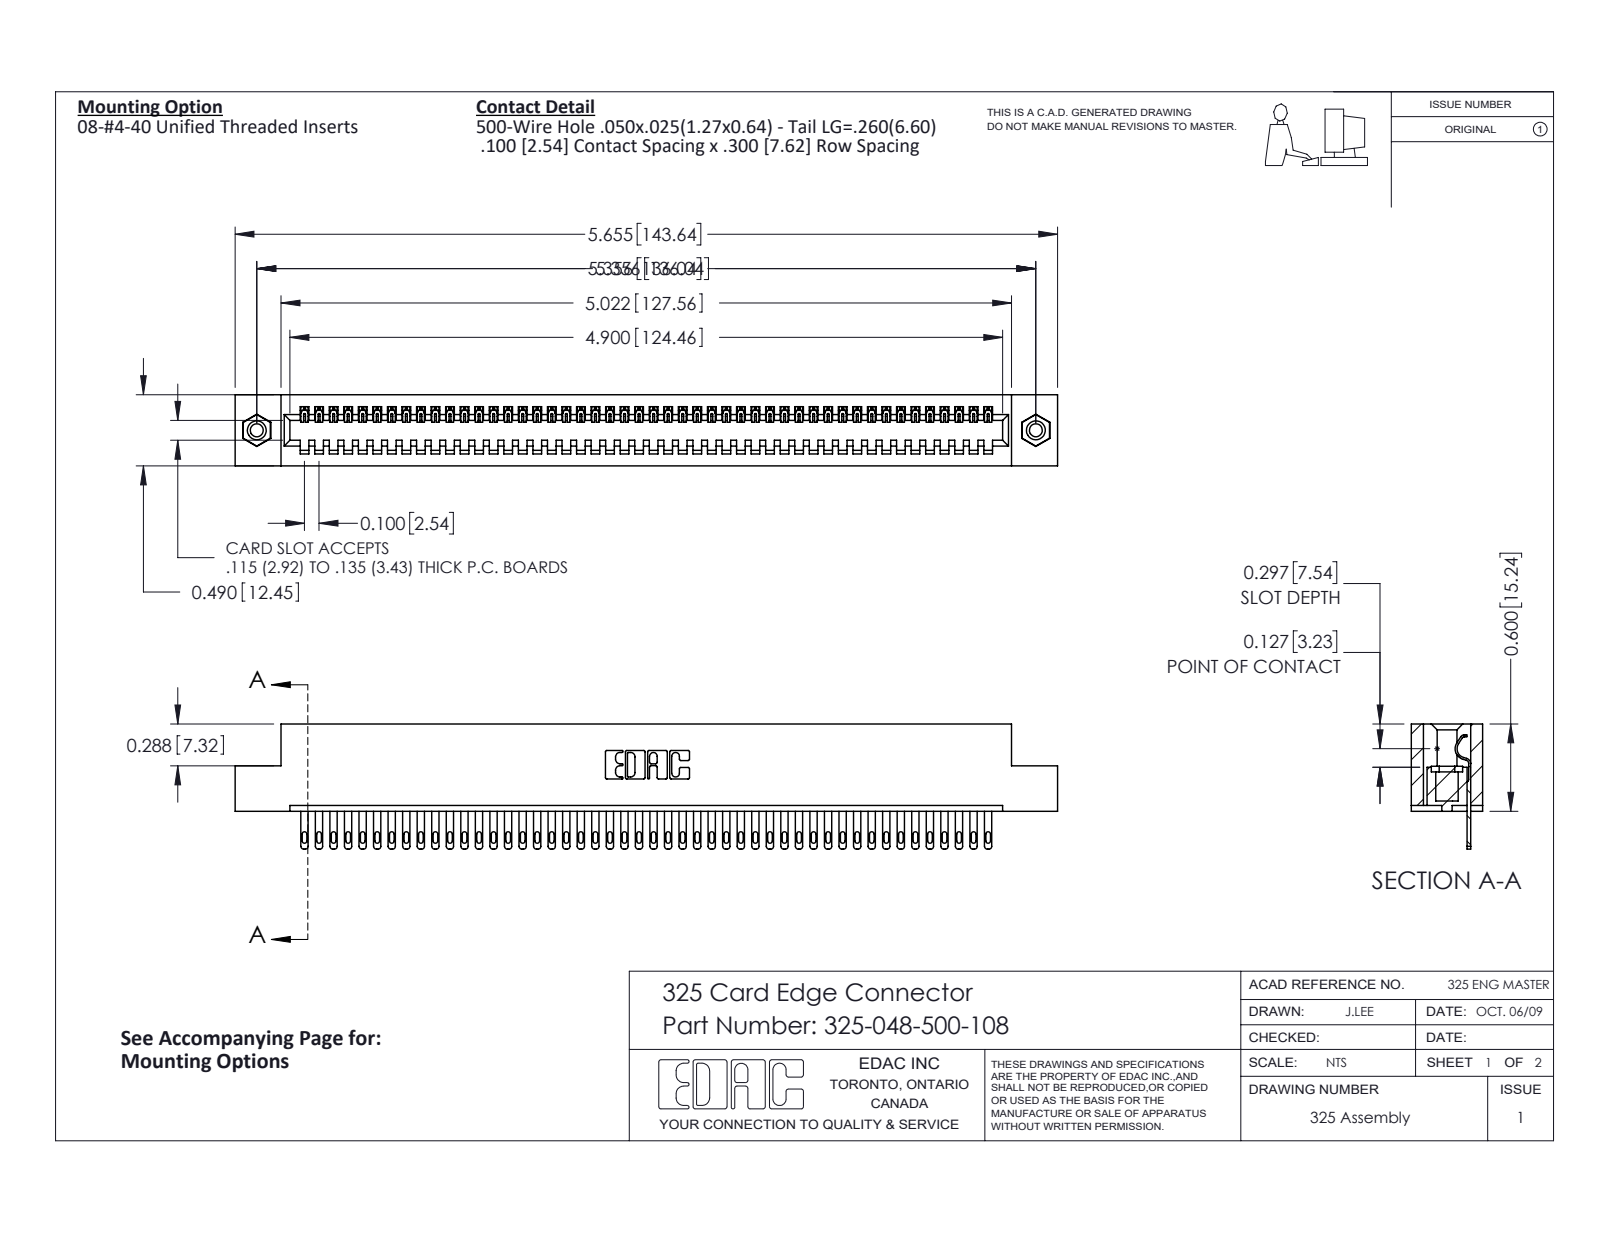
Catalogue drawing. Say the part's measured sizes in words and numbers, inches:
The part is named "325-048-500-108; 345-250-001_345-250-003-102; 325-292-001_325-293-100; 325 Part_TI". Its 3-D file was written by "SolidWorks 2016 (CONFIG_CONTROL_DESIGN)". It is 51 solids with 2766 faces: 1830 planar, 920 cylindrical and 16 other. Overall it measures 5.655 by 0.86 by 0.49 inches. Its volume is 1.117 cubic inches and its surface area 31.35 square inches. Round holes: 2 of diameter 0.089, 2 of diameter 0.125, 2 of diameter 0.16. Round bosses or shafts: 2 of diameter 0.155. Partial cylindrical surfaces (rounded edges, fillets, slot ends): 96 of radius 0.006, 96 of radius 0.016, 96 of radius 0.02, 22 of radius 0.01, 6 of radius 0.007, 6 of radius 0.031, 3 of radius 0.026, 1 of radius 0.014. The main face-to-face distances are 0.083, 0.407, 0.49, 0.3, 0.107, 0.383, 0.025, 0.325, 0.56, 0.263. The hole center spacings are 5.356.
